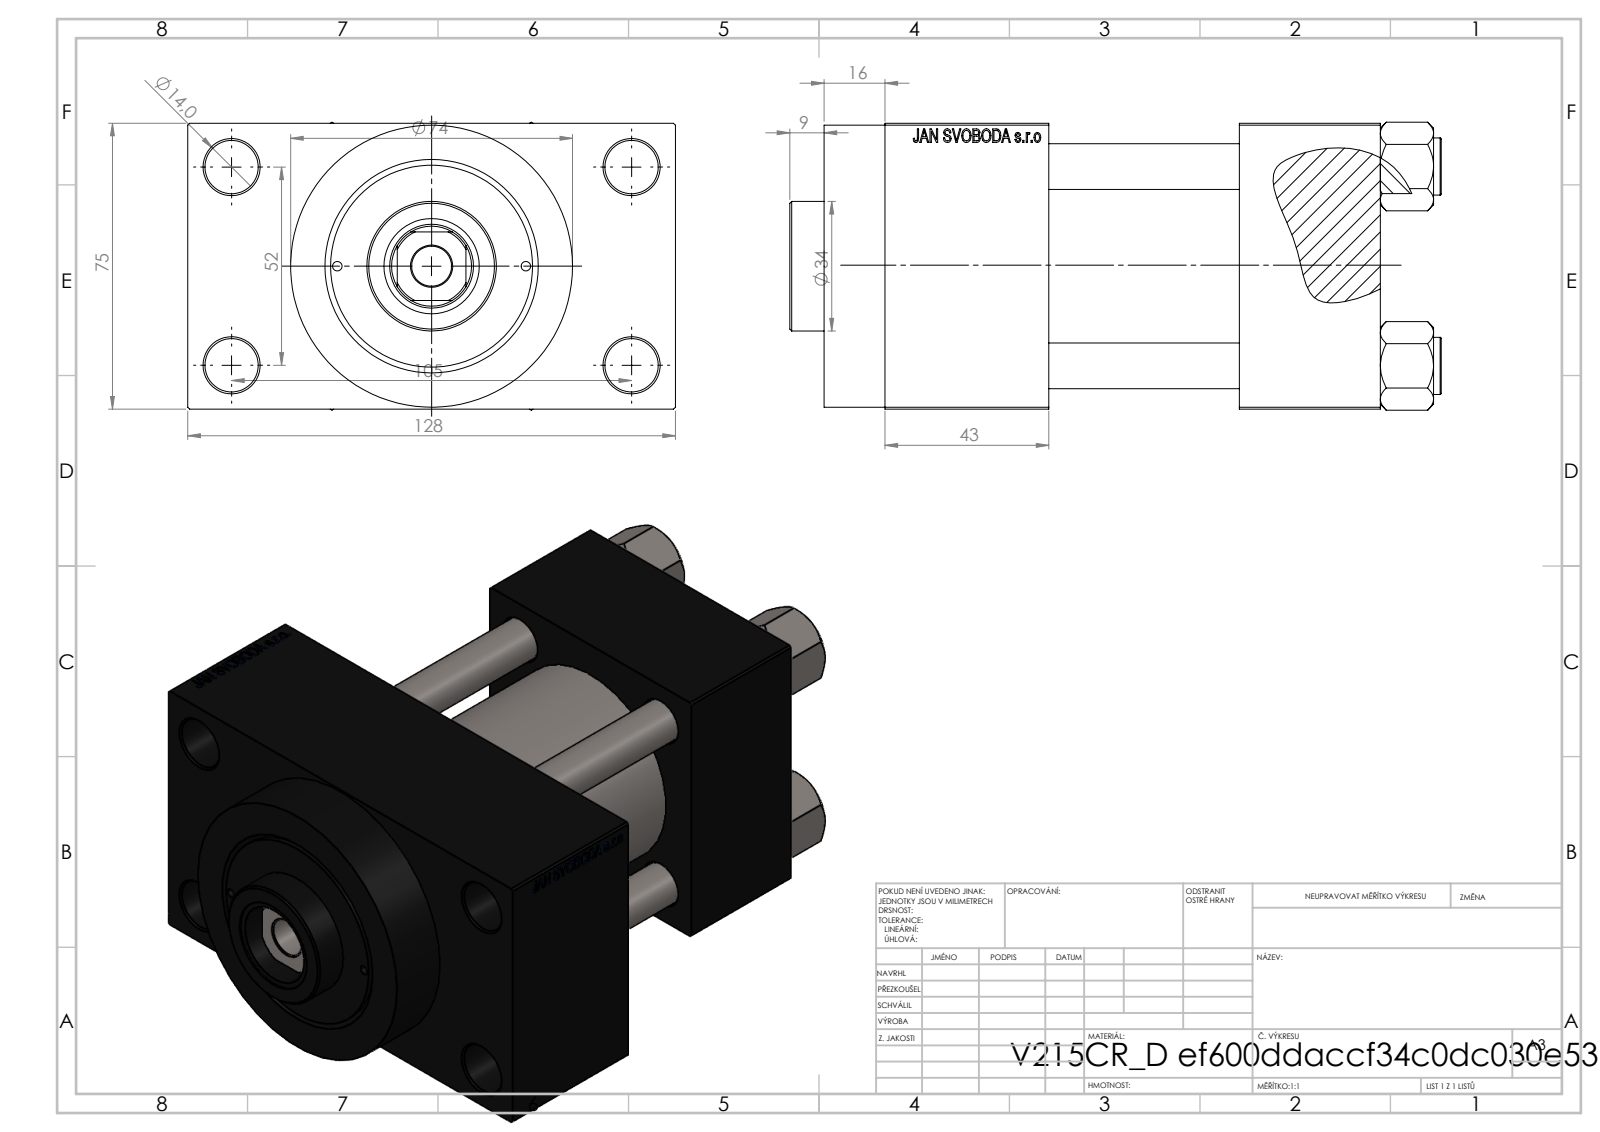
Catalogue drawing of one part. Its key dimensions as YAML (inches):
part_name: "V215CR_D_TYCINKA; V215_VC_A; NUT_M5_D; V215CR_D_Body (+1 more)"
step_written_by: "SolidWorks 2019 (CONFIG_CONTROL_DESIGN)"
units: inches
bodies: {solids: 11, faces: 1111, planar: 499, cylindrical: 92, other: 520}
overall_size: [6.732, 5.039, 2.974]
volume: 46.45
surface_area: 247.7
round_holes:
  - {diameter: 0.472, count: 4}
  - {diameter: 0.551, count: 4}
  - {diameter: 0.098, count: 2}
  - {diameter: 0.276, count: 2}
  - {diameter: 0.825, count: 2}
  - {diameter: 1.181, count: 2}
  - {diameter: 0.413, count: 1}
  - {diameter: 0.866, count: 1}
  - {diameter: 0.984, count: 1}
  - {diameter: 1.614, count: 1}
  - {diameter: 1.969, count: 1}
  - {diameter: 2.087, count: 1}
round_bosses_or_shafts:
  - {diameter: 0.591, count: 4}
  - {diameter: 2.913, count: 1}
  - {diameter: 2.205, count: 1}
  - {diameter: 1.339, count: 1}
partial_cylinders:
  - {radius: 0.413, count: 1}
face_to_face_distances: [2.953, 1.969, 1.457, 3.425, 1.043, 5.118, 3.661, 1.693, 3.996, 0.63]
hole_center_spacings: [1.031, 1.037, 1.456, 1.497, 2.059, 2.253, 2.3, 2.307]
